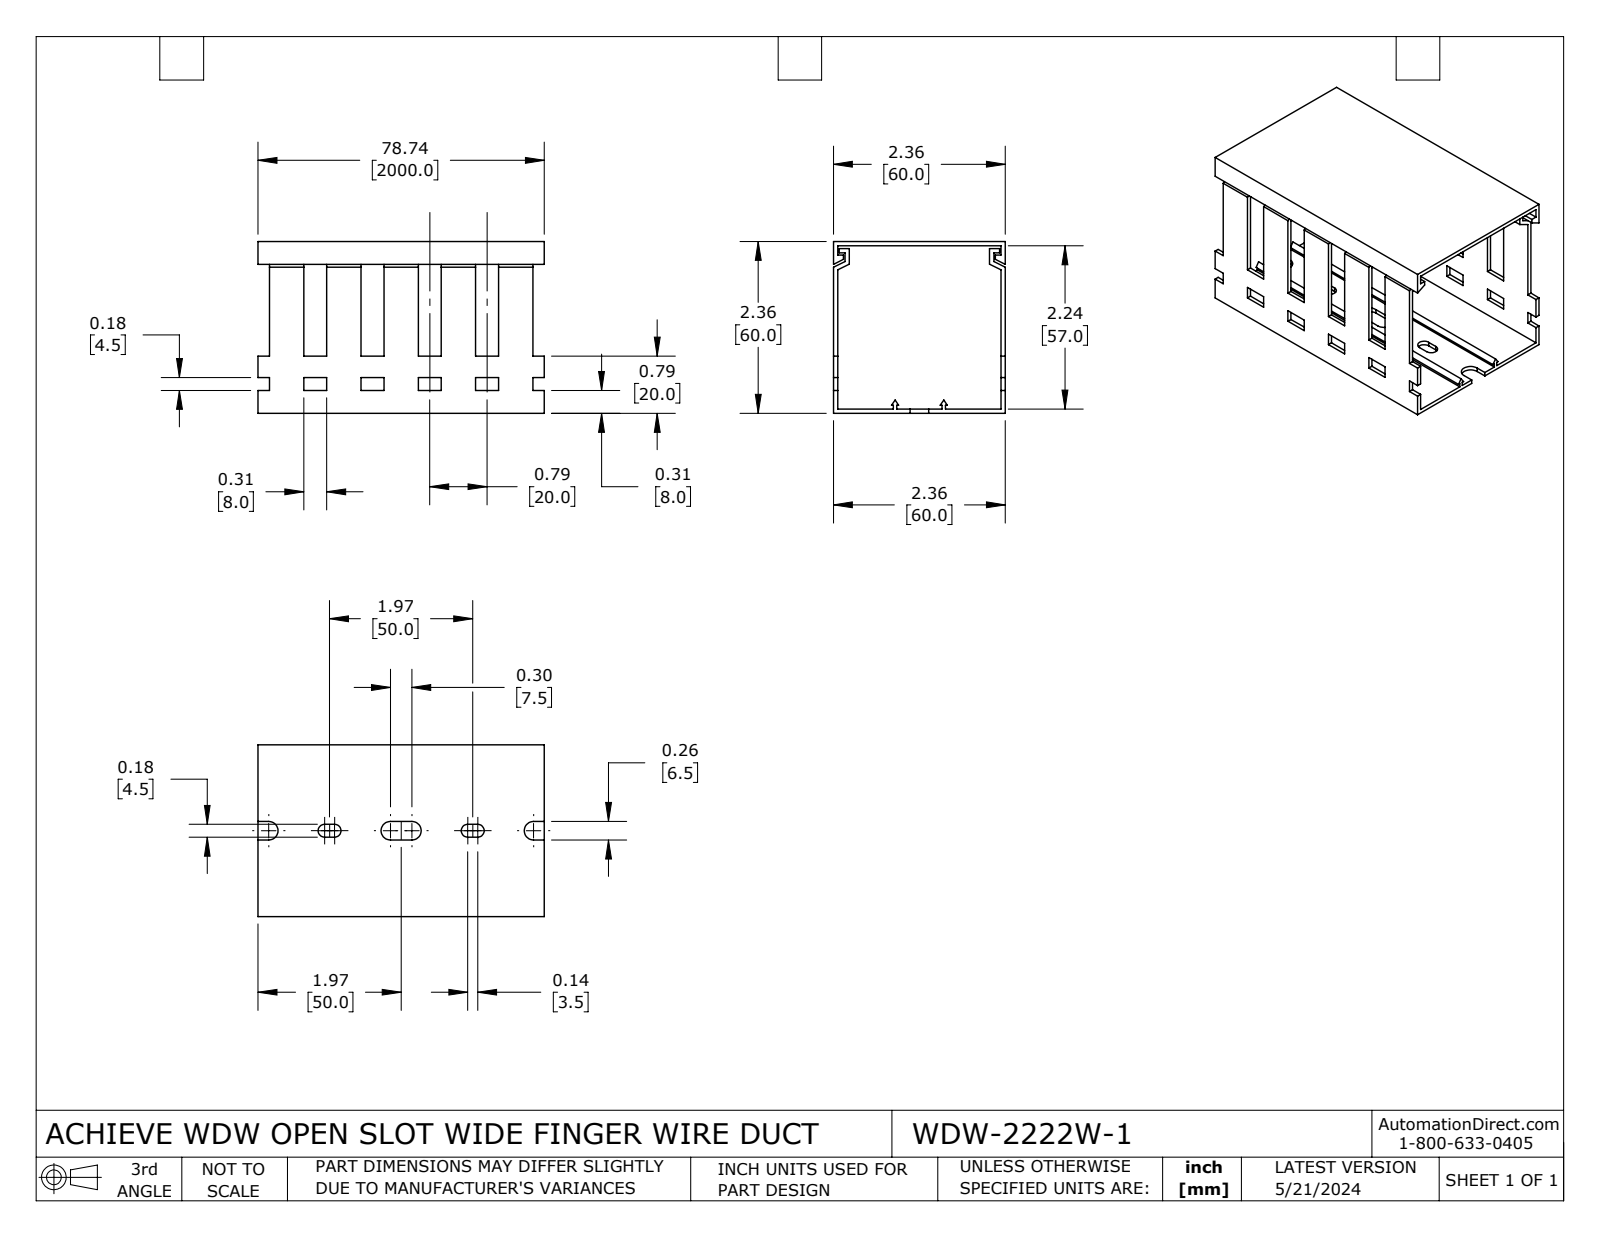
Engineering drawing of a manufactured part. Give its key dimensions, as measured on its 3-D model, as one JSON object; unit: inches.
{"part_name": "WDW-2222W-1", "step_written_by": "SolidWorks 2023 (CONFIG_CONTROL_DESIGN)", "units": "inches", "bodies": {"solids": 2, "faces": 210, "planar": 198, "cylindrical": 12, "other": 0}, "overall_size": [3.937, 2.362, 2.362], "volume_in3": 2.052, "surface_area_in2": 74.03, "partial_cylinders_radius": [[0.089, 4], [0.128, 4]], "face_to_face_distances": [0.059, 2.303, 2.362, 2.244, 0.157, 2.146, 2.205, 0.787, 0.098, 0.079]}
